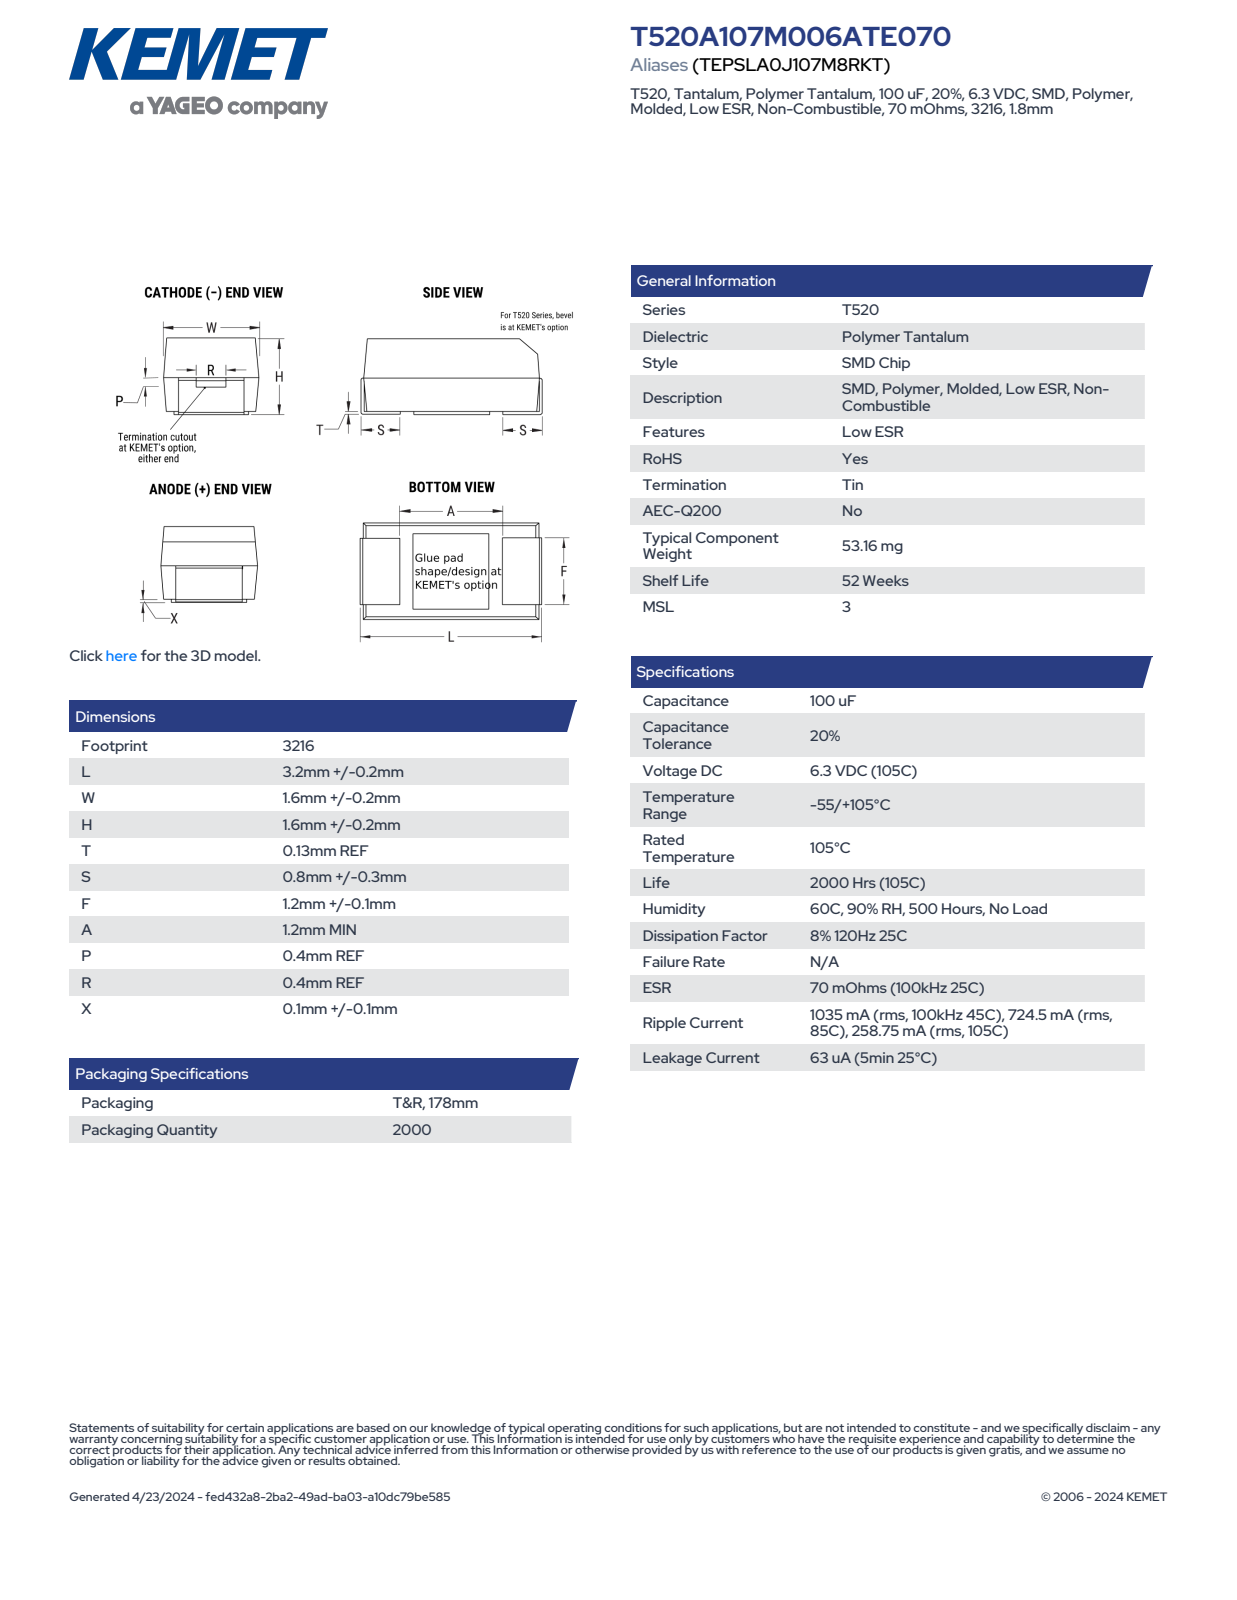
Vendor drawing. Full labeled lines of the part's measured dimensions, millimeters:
Part name (STEP PRODUCT): Case_Anode_18; CTS_3216_L3.40W1.80H1.80S0.8F1.2R0.4P0.4; Case_Top_18; Case_Cathode_18 (+1 more)
STEP written by: SolidWorks 2014 (AUTOMOTIVE_DESIGN)
Units: millimetres
Bodies: 4 solids, 42 faces (37 planar, 5 cylindrical, 0 other)
Overall size (bounding box): 3.4 × 1.8 × 1.8
Volume: 9 mm³ · Surface area: 46 mm²
Main face-to-face distances: 0.75, 1.67, 0.92, 1.8, 1.79, 0.85, 1.77, 0.88, 3.27, 3.13
